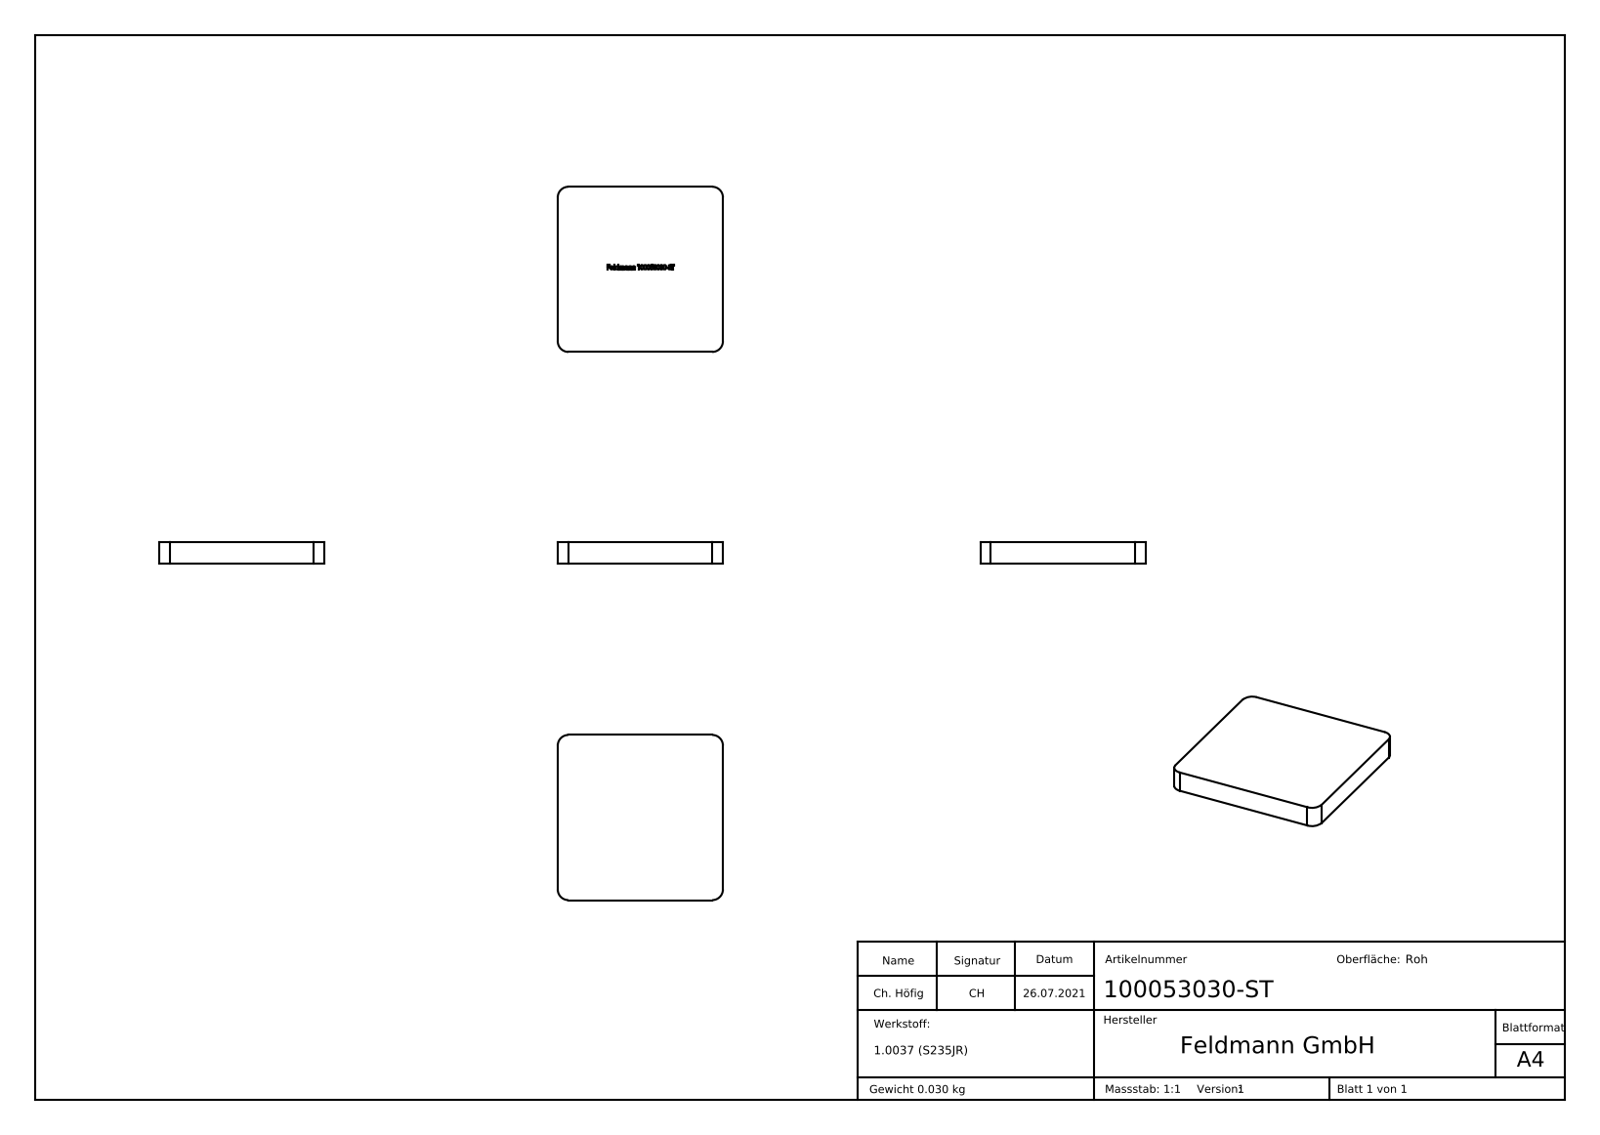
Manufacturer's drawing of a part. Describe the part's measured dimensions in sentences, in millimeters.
The part is named "100053030-ST". Its 3-D file was written by "SolidWorks 2018 (CONFIG_CONTROL_DESIGN)". It is 1 solid with 268 faces: 120 planar, 4 cylindrical and 144 other. Overall it measures 31 by 31 by 4 millimeters. Its volume is 3 830 cubic millimeters and its surface area 2 404 square millimeters. Partial cylindrical surfaces (rounded edges, fillets, slot ends): 4 of radius 2. The main face-to-face distances are 4, 31, 3.9, 15.5, 1.78, 4.61, 1.21, 10.93, 6.32, 5.82.
